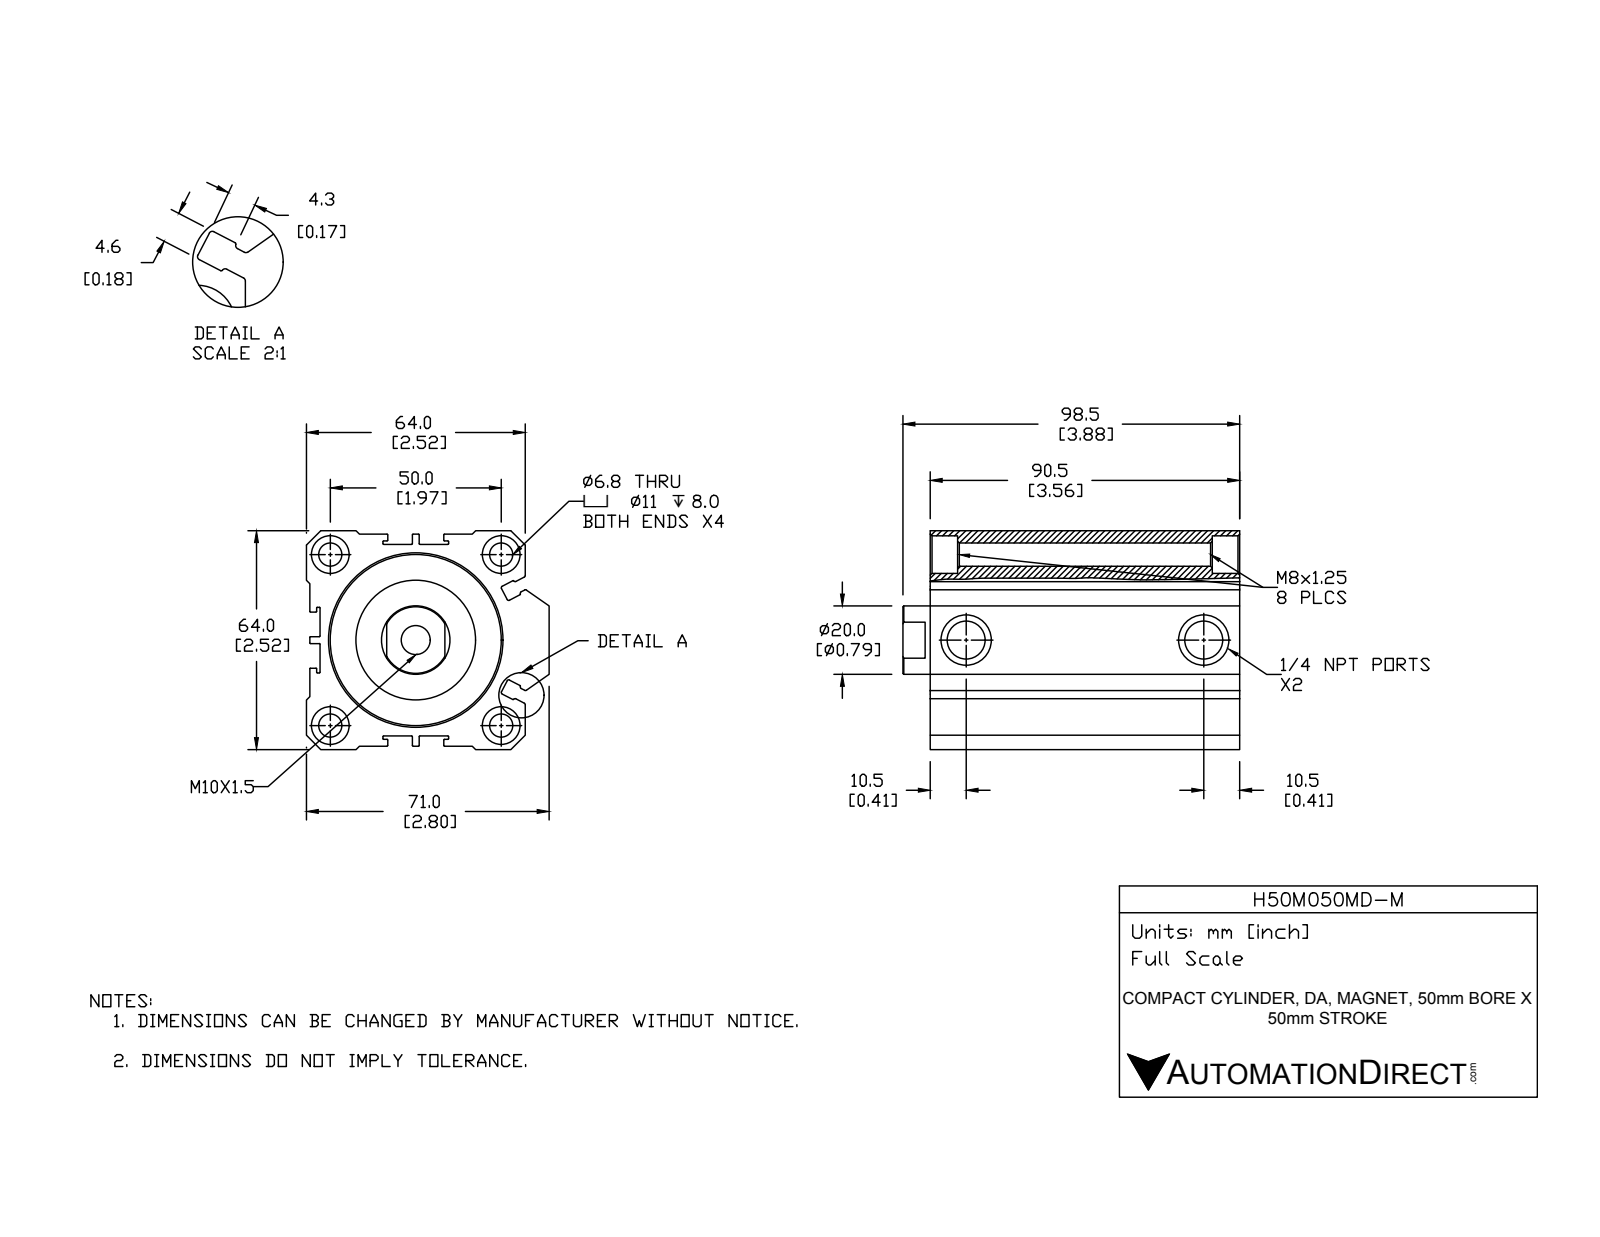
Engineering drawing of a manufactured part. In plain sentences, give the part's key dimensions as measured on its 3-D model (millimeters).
The part is named "H50M050MD-M; H50M050MD-M-BODY; H50M050MD-M-PISTON". Its 3-D file was written by "SolidWorks 2015 (CONFIG_CONTROL_DESIGN)". It is 2 solids with 255 faces: 99 planar, 103 cylindrical and 53 other. Overall it measures 98.5 by 71 by 64 millimeters. Its volume is 243 470 cubic millimeters and its surface area 76 067 square millimeters. Round holes: 4 of diameter 6.8, 4 of diameter 11, 2 of diameter 11.13, 1 of diameter 8.5, 1 of diameter 20, 1 of diameter 36, 1 of diameter 50. Round bosses or shafts: 1 of diameter 35, 1 of diameter 31. Partial cylindrical surfaces (rounded edges, fillets, slot ends): 40 of radius 0.2, 12 of radius 0.5. The main face-to-face distances are 4, 1, 60, 3, 63, 64, 71, 7, 59, 30. The hole center spacings are 35.36, 50, 70.71, 69.5.
